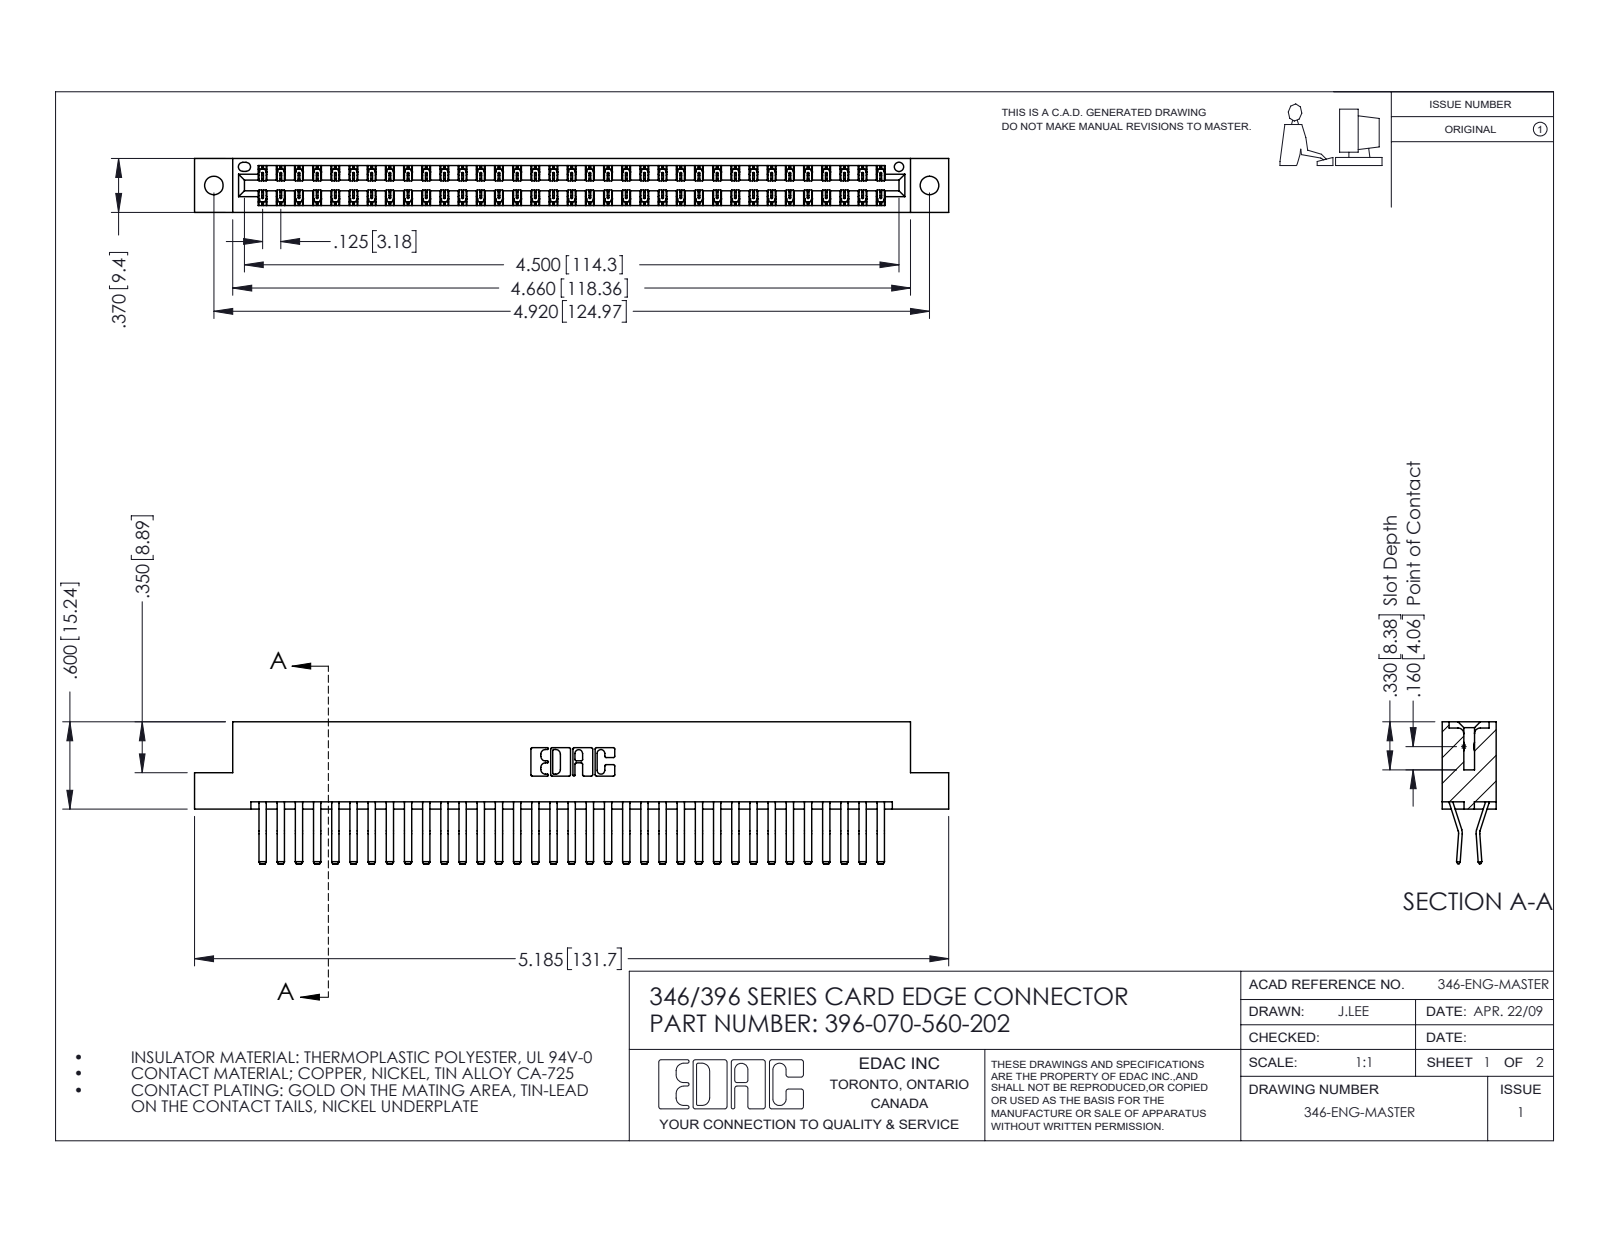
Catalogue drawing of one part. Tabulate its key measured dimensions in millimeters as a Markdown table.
| quantity | value |
| --- | --- |
| part name | 396-070-560-202; 345-292-001_560 Tail; 346 Part_Flush Mounting Lugs - 0.128 Dia |
| STEP written by | SolidWorks 2016 (CONFIG_CONTROL_DESIGN) |
| units | millimeters |
| bodies | 71 solids, 3902 faces (2526 planar, 1376 cylindrical, 0 other) |
| overall size | 131.7 × 24.8 × 9.4 |
| volume | 13 200 mm³ |
| surface area | 19 000 mm² |
| round holes (diameter × count) | 3.3 × 2, 1.6 × 1 |
| partial cylindrical surfaces (radius × count) | 0.2 × 105, 0.3 × 22, 0.2 × 6, 0.8 × 6, 0.7 × 3, 0.3 × 2, 0.4 × 2, 0.6 × 2 |
| main face-to-face distances | 1.2, 8.2, 9.4, 0.6, 6.4, 1.8, 7.6, 7, 3.8, 5.6 |
| hole center spacings | 6.2, 119.7, 125 |
